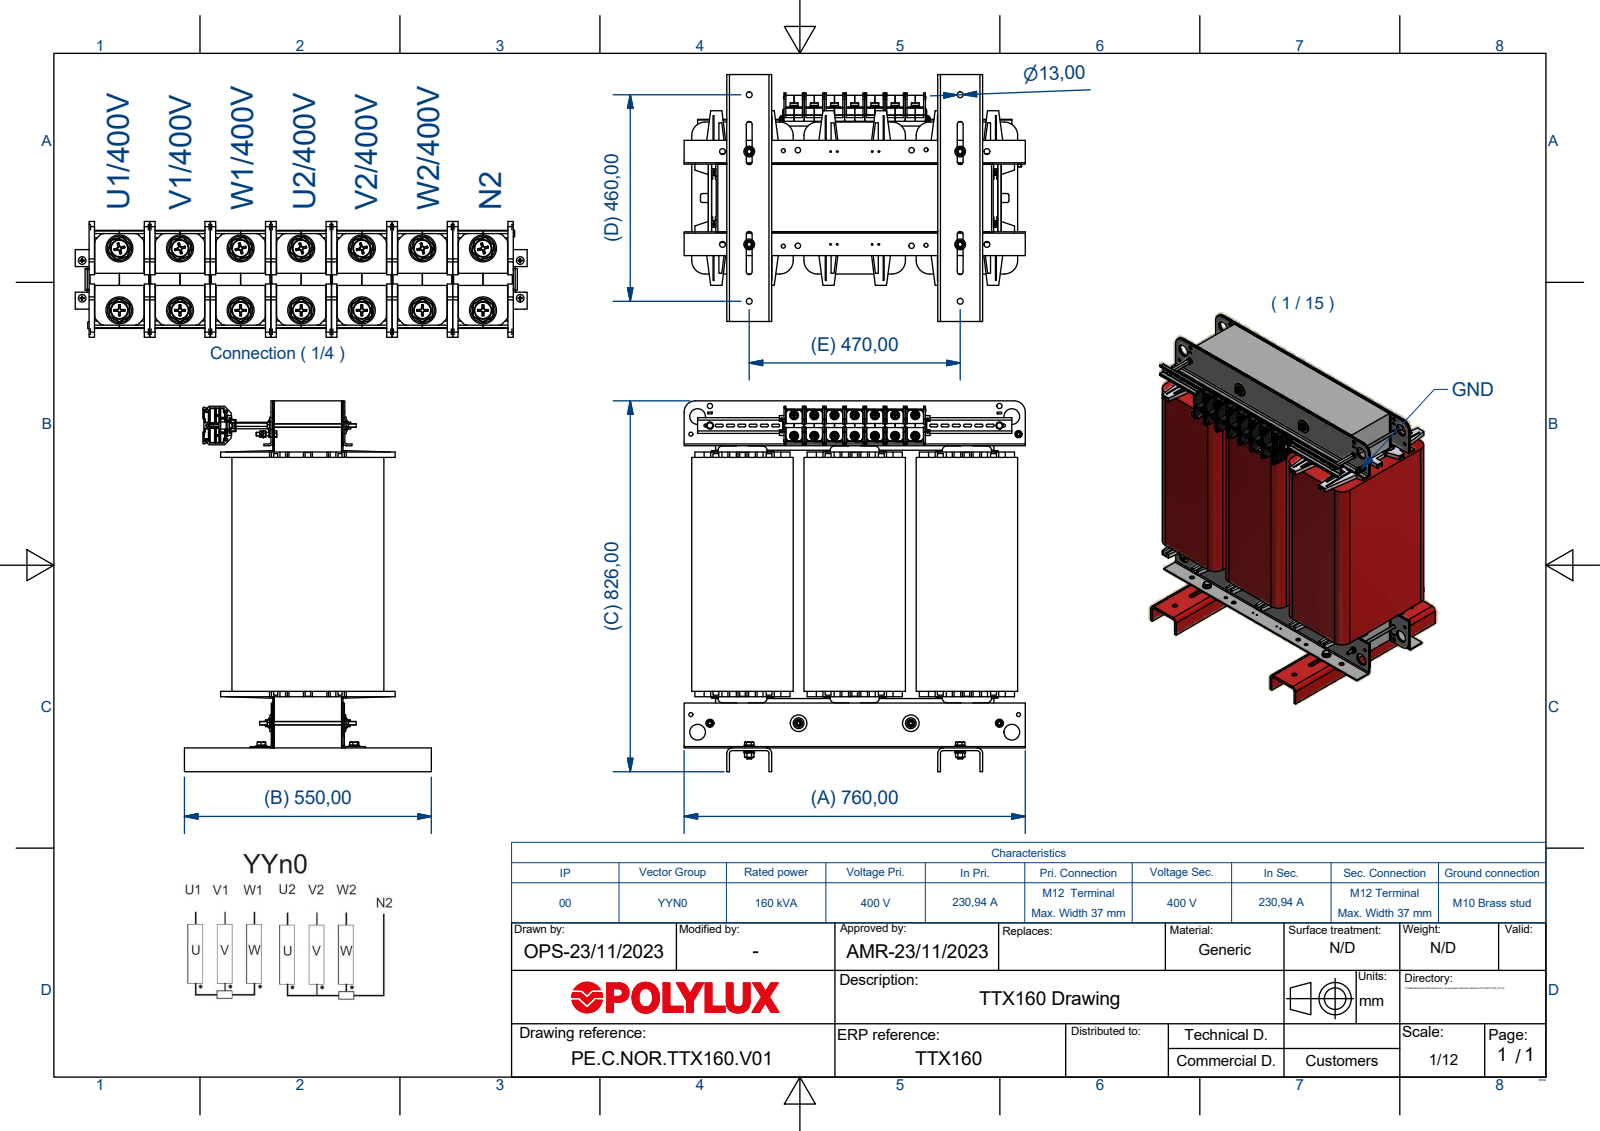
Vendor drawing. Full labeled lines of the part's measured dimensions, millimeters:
Part name (STEP PRODUCT): TTX160_V01
STEP written by: Autodesk Inventor 2018 (AUTOMOTIVE_DESIGN)
Units: millimetres
Bodies: 192 solids, 10548 faces (8278 planar, 1545 cylindrical, 725 other)
Overall size (bounding box): 773 × 760 × 428.39
Volume: 137 200 000 mm³ · Surface area: 9 001 000 mm²
Round holes (diameter × count): ⌀12 ×18, ⌀8.5 ×15, ⌀10.5 ×14, ⌀10.7 ×14, ⌀11.5 ×14, ⌀12.25 ×14, ⌀13 ×12, ⌀6.65 ×9, ⌀3.5 ×8, ⌀9 ×8, ⌀8.4 ×7, ⌀16 ×4
Round bosses / shafts (diameter × count): ⌀20 ×14, ⌀18.1 ×14, ⌀9.85 ×14, ⌀8 ×9, ⌀37 ×4, ⌀24 ×4, ⌀3.92 ×4, ⌀3 ×4
Partial cylindrical surfaces — rounded edges, fillets, slot ends (radius × count): R0.5 ×154, R1 ×74, R4 ×58, R3 ×56, R10 ×24, R3.75 ×16, R0.93 ×14, R8 ×14
Main face-to-face distances: 250, 3, 3.25, 153.5, 150.25, 153.25, 168, 500, 58, 45.75
Hole centre spacings: 250, 206.75, 241.39, 473.3, 15, 32.35, 34, 36.17
